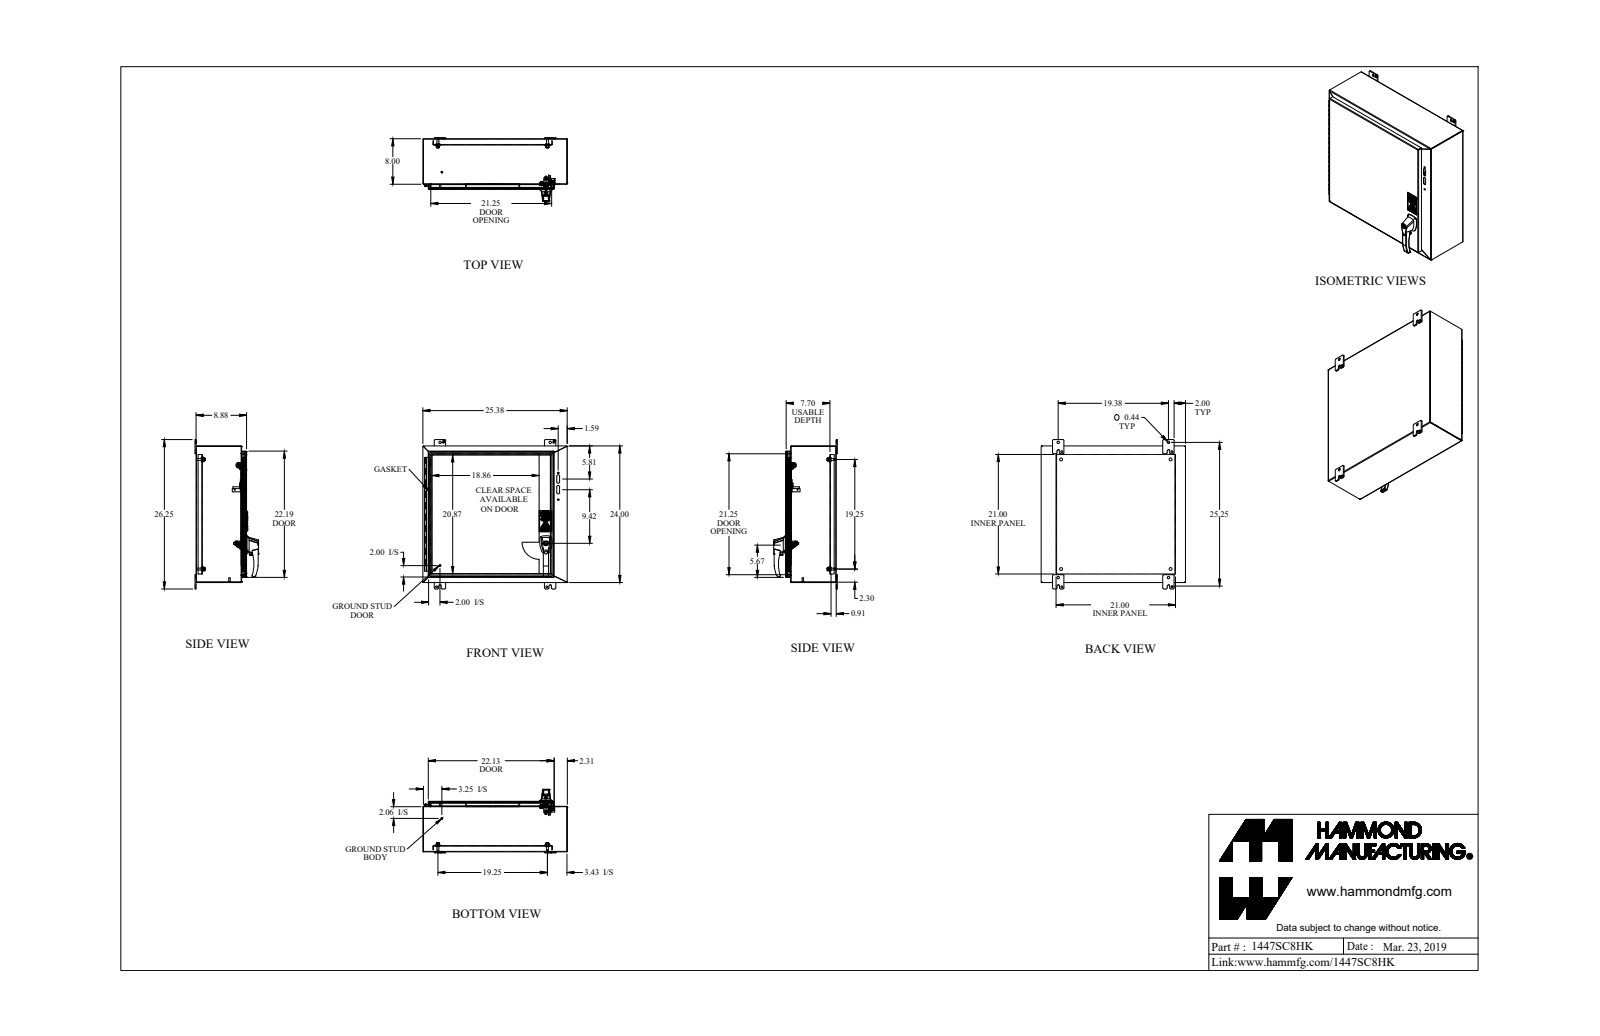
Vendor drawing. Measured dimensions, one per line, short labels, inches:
name: 1447SC8HK
written by: SolidWorks 2019 (AUTOMOTIVE_DESIGN)
unit: in
bodies: 49 solids, 1157 faces (711 planar, 331 cylindrical, 115 other)
size: 26.25 × 25.375 × 11.177
volume: 230.3 in³; area: 5 745 in²
holes: 5× ⌀0.313, 4× ⌀0.176, 4× ⌀0.437, 4× ⌀0.5, 2× ⌀0.156, 2× ⌀0.173, 2× ⌀0.215, 2× ⌀0.25, 2× ⌀0.265, 2× ⌀0.281, 2× ⌀0.307, 2× ⌀0.413
bosses: 8× ⌀0.375, 7× ⌀0.25, 4× ⌀1, 4× ⌀0.65, 4× ⌀0.33, 4× ⌀0.156, 2× ⌀0.5, 2× ⌀0.402
rounds: 28× R0.079, 24× R0.188, 16× R0.007, 12× R0.25, 11× R0.125, 8× R0.03, 8× R0.151, 8× R0.218
face distances: 0.072, 8.803, 8.731, 8.875, 0.095, 7.771, 7.699, 1.032, 1.104, 7.866
hole spacings: 19.25, 19.375, 1.111, 1.735, 1.736, 1.855, 13.969, 15.524
